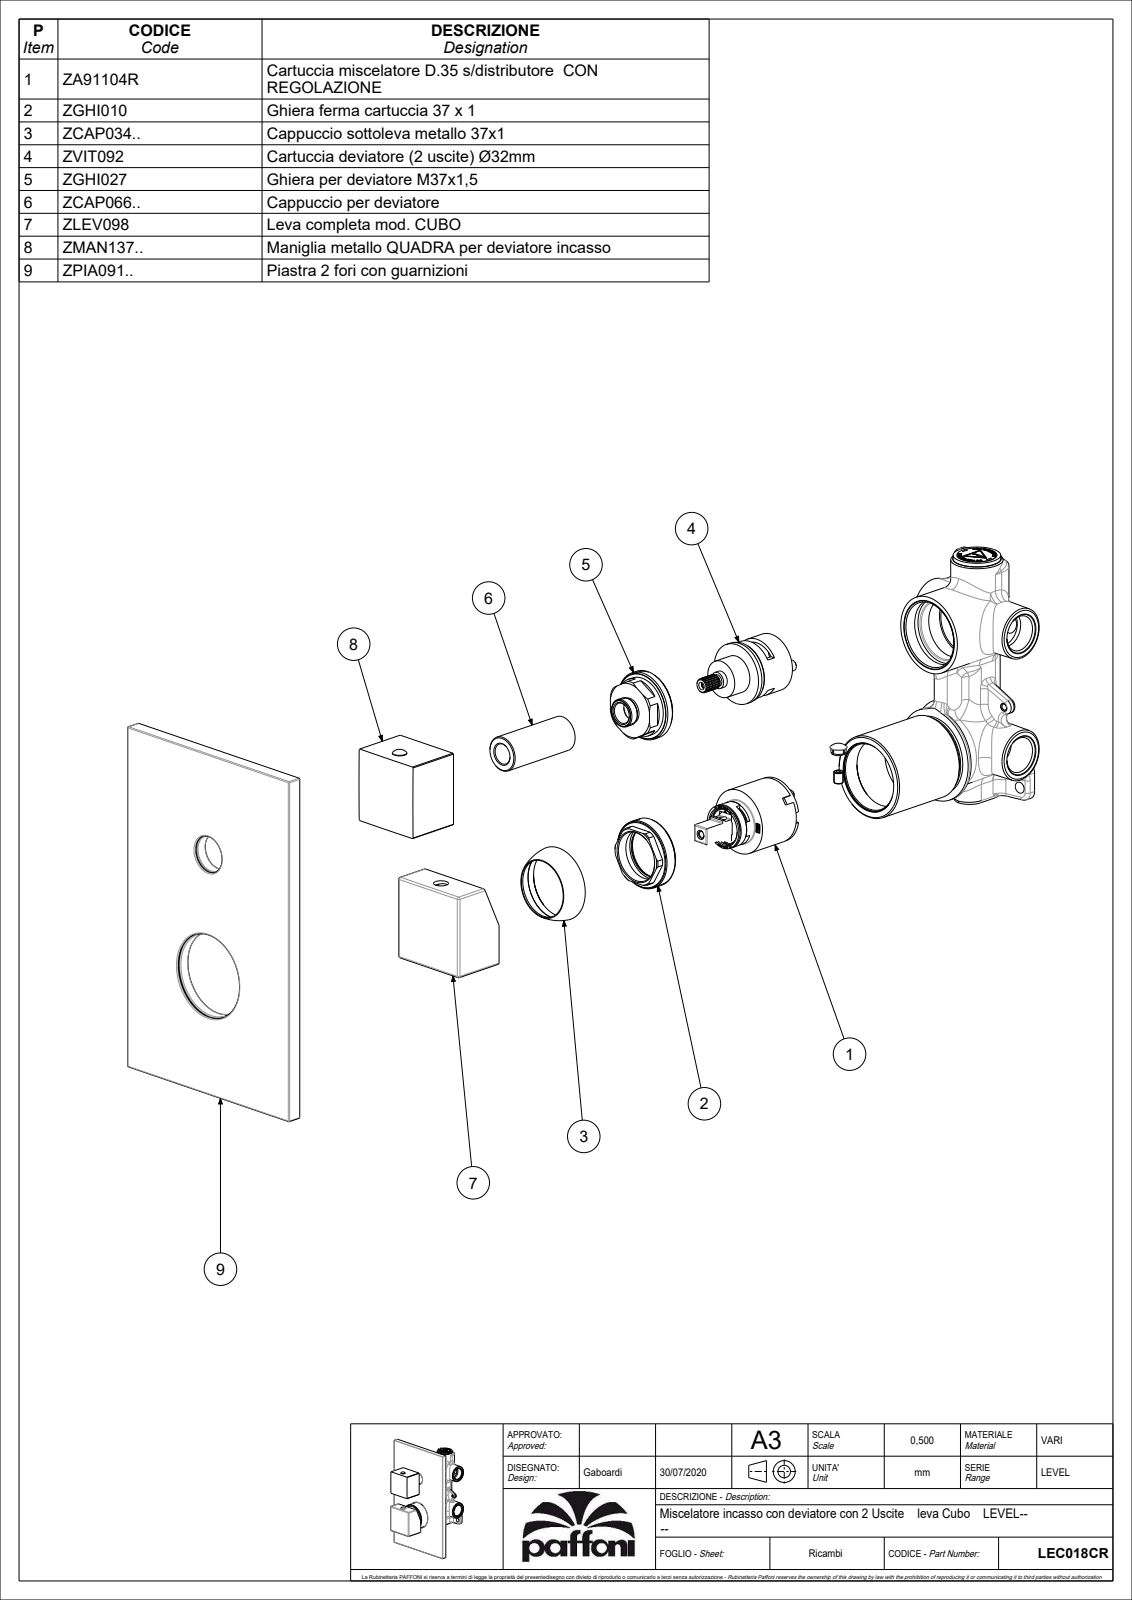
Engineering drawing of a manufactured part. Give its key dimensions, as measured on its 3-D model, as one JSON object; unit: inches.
{"part_name": "LEC018CR", "step_written_by": "CREO PARAMETRIC BY PTC INC, 2020044 (CONFIG_CONTROL_DESIGN)", "units": "inches", "bodies": {"solids": 4, "faces": 1071, "planar": 607, "cylindrical": 278, "other": 186}, "overall_size": [7.48, 4.724, 2.22], "volume_in3": 12.32, "surface_area_in2": 202.1, "round_holes": [[0.157, 2], [0.433, 2], [1.417, 2], [0.118, 1], [0.126, 1], [0.13, 1], [0.165, 1], [0.177, 1], [0.197, 1], [0.217, 1], [0.236, 1], [0.583, 1]], "round_bosses_or_shafts": [[0.197, 2], [2.008, 1], [1.929, 1], [1.764, 1], [1.378, 1], [0.984, 1], [0.925, 1], [0.921, 1]], "partial_cylinders_radius": [[0.039, 18], [0.02, 14], [0.006, 11], [0.012, 4], [0.156, 1], [0.276, 1], [0.366, 1], [0.427, 1]], "face_to_face_distances": [0.098, 0.217, 0.315, 0.02, 0.118, 0.197, 1.575, 1.835, 3.15, 1.476], "hole_center_spacings": [0.028, 0.394, 0.555, 0.583, 2.283, 2.677]}
